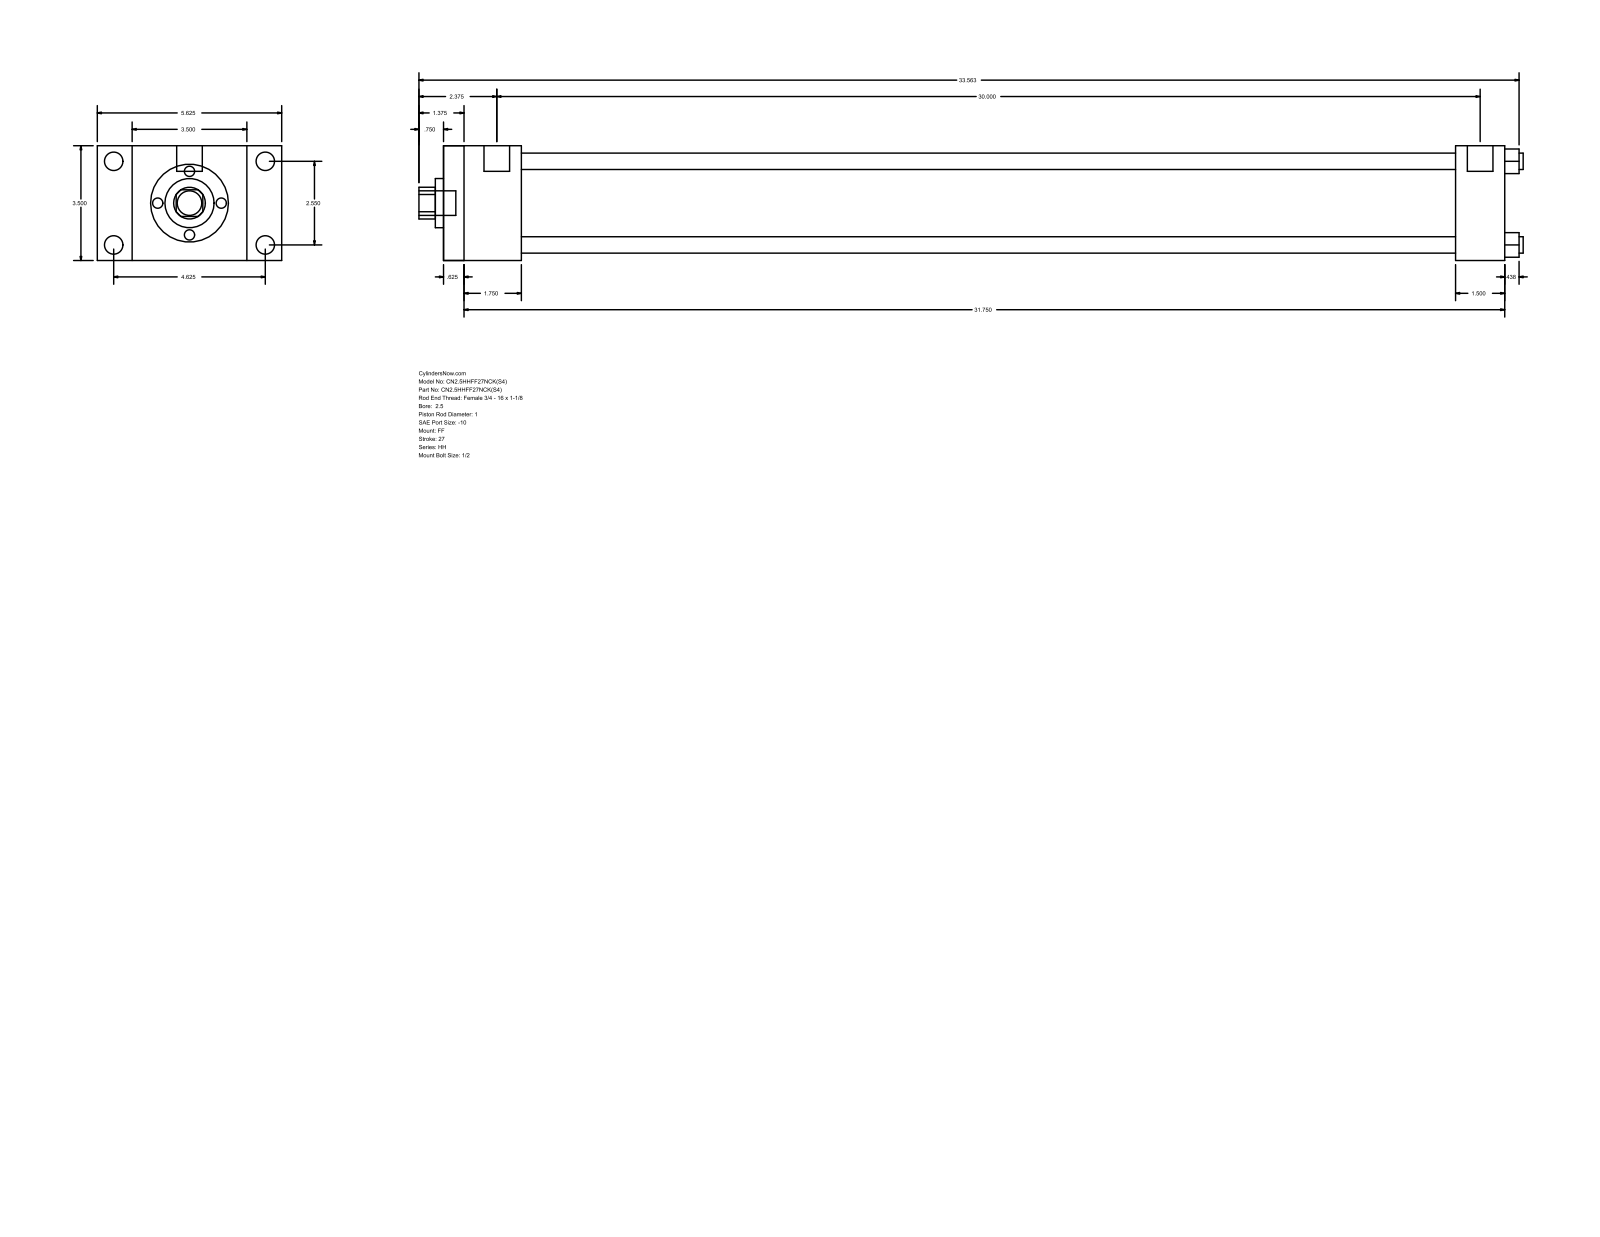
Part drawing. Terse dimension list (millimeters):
name: HH_FF__0250_1
written by: GSSL Pune (CONFIG_CONTROL_DESIGN)
unit: mm
bodies: 0 solids, 92 faces (64 planar, 28 cylindrical, 0 other)
size: 855.66 × 142.88 × 88.9
holes: 4× ⌀12.7, 1× ⌀25.4, 1× ⌀38.1, 1× ⌀73.03
bosses: 4× ⌀14.3, 4× ⌀5.56, 2× ⌀19.84, 1× ⌀19.05
rounds: 1× R12.29
face distances: 88.9, 822.33, 15.87, 806.46, 60.33, 44.46, 762, 784.22, 768.35, 723.89
hole spacings: 45.79, 64.76, 91.58
